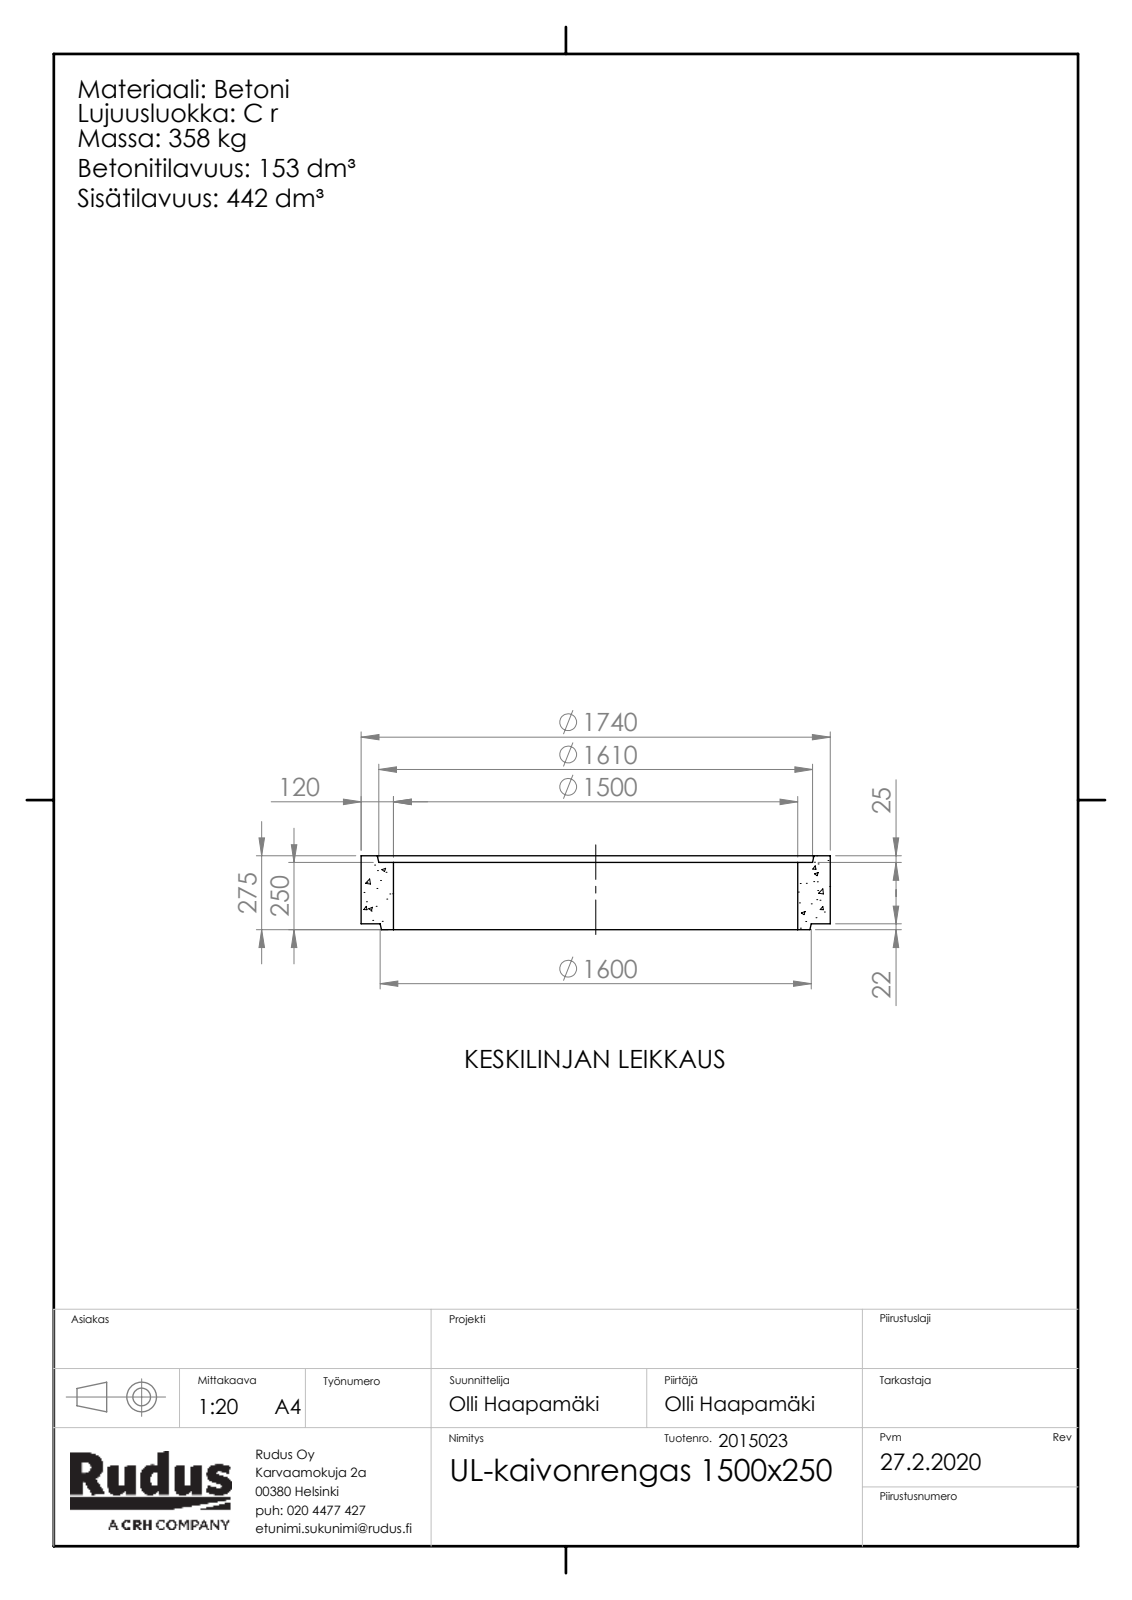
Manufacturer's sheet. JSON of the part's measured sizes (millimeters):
{"part_name": "EK-osa-kaivorunko_UL-kaivonrengas; Rudus 2015023 UL-kaivonrengas 1500x250", "step_written_by": "SolidWorks 2019 (CONFIG_CONTROL_DESIGN)", "units": "millimeters", "bodies": {"solids": 1, "faces": 89, "planar": 8, "cylindrical": 0, "other": 81}, "overall_size": [1740, 1740, 275], "volume_mm3": 152600000, "surface_area_mm2": 3979000, "face_to_face_distances": [253, 228, 25, 22, 250, 275, 137.5, 115.5, 112.5, 186.73]}
